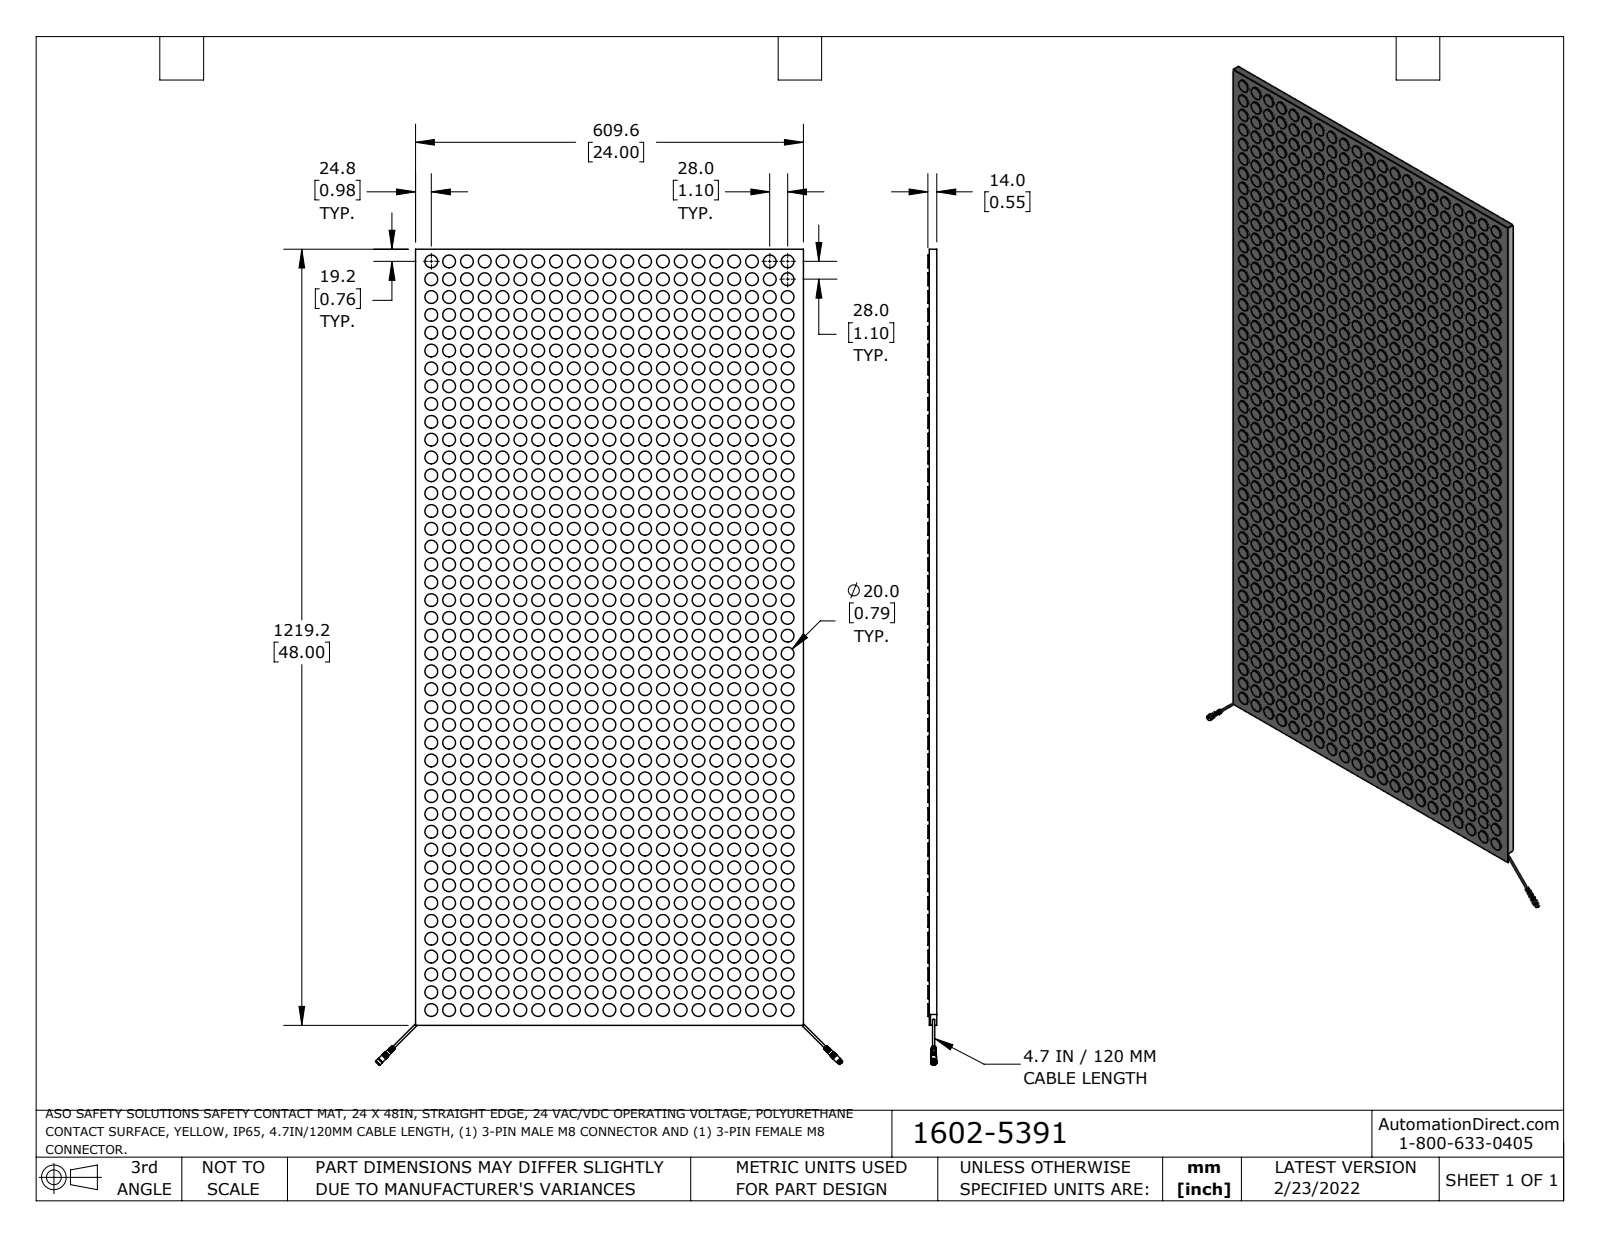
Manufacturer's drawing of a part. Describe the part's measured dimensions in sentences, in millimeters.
The part is named "1602-5391_Default". Its 3-D file was written by "SolidWorks 2021 (CONFIG_CONTROL_DESIGN)". It is 20 solids with 3093 faces: 1031 planar, 1924 cylindrical and 138 other. Overall it measures 1282 by 734.2 by 14 millimeters. Its volume is 9 488 000 cubic millimeters and its surface area 1 649 000 square millimeters. Round holes: 3 of diameter 1.6, 2 of diameter 3.4, 2 of diameter 6.9, 1 of diameter 5.8, 1 of diameter 5.9, 1 of diameter 7.2. Round bosses or shafts: 903 of diameter 20, 24 of diameter 1.2, 8 of diameter 0.8, 3 of diameter 1, 2 of diameter 9, 2 of diameter 8.8, 2 of diameter 6.8, 2 of diameter 3.5. The main face-to-face distances are 12, 2, 14, 609.6, 1219.2, 2.2, 10, 4, 4.4, 1. The hole center spacings are 1.8, 2.5, 3.5.
